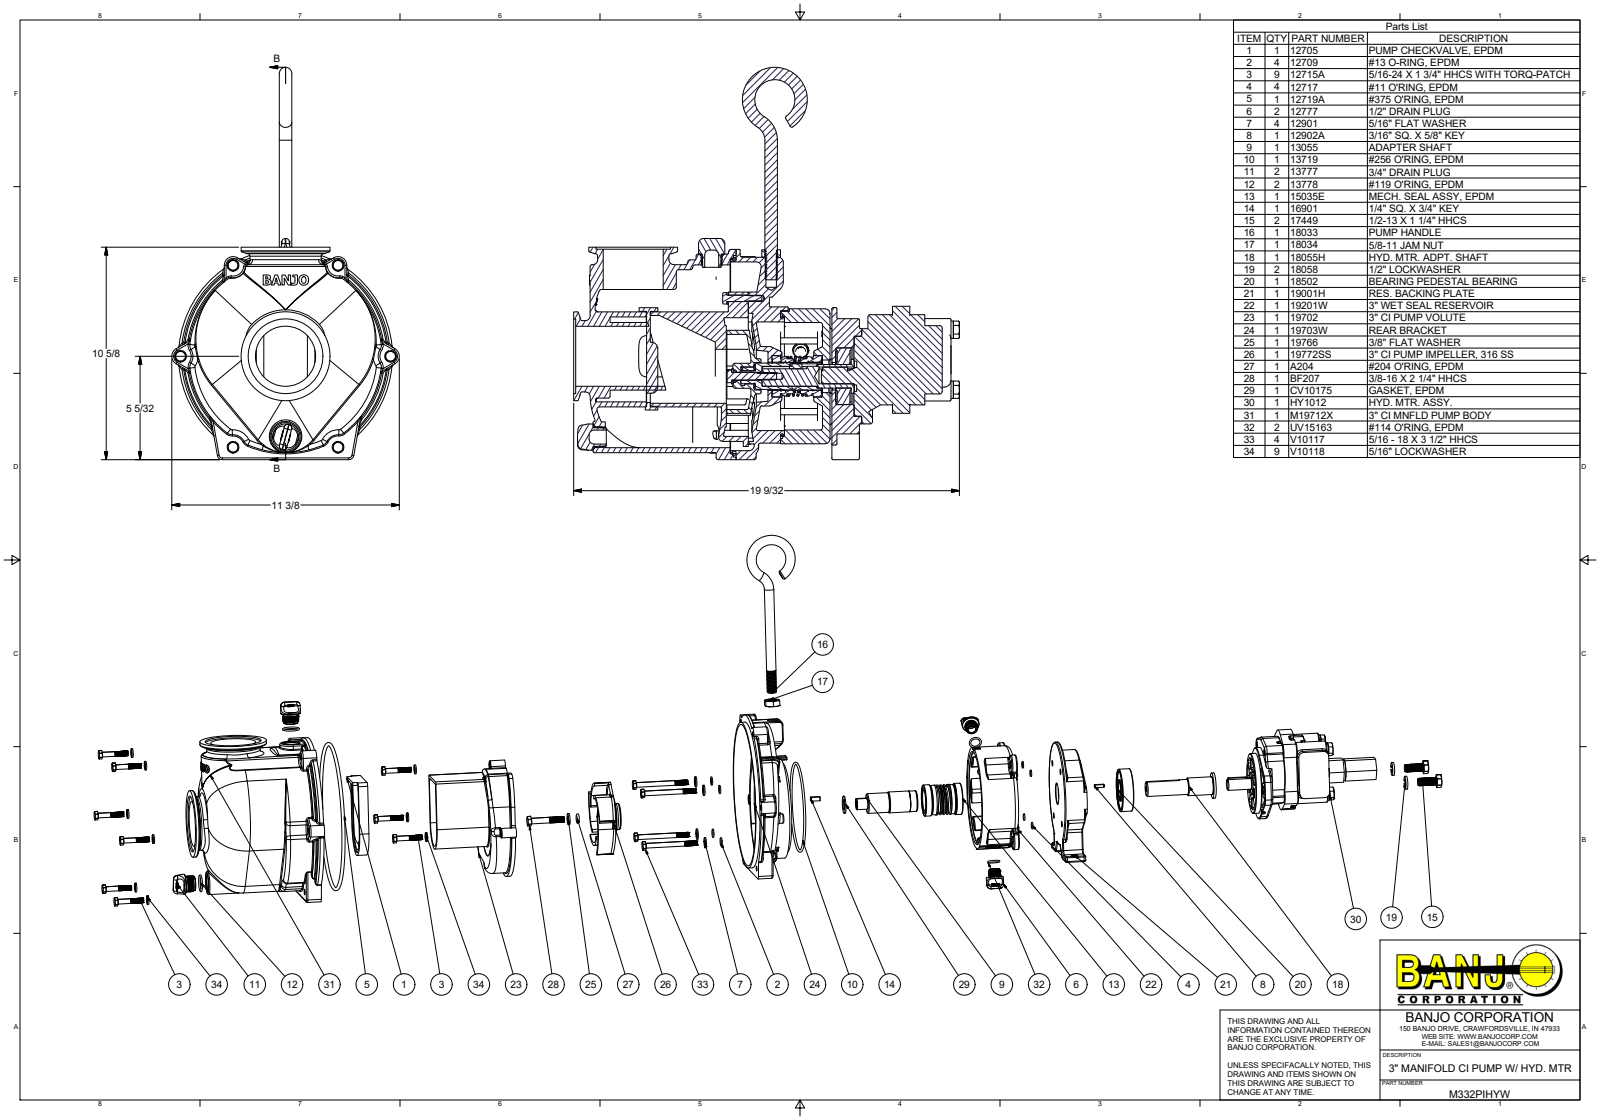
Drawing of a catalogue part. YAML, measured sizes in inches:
part_name: "M332PIHYW; 19703W; 19201W; M19712X (+8 more)"
step_written_by: "Autodesk Inventor 2012 (AUTOMOTIVE_DESIGN)"
units: inches
bodies: {solids: 74, faces: 8066, planar: 1729, cylindrical: 2662, other: 3675}
overall_size: [22.172, 19.62, 11.375]
volume: 382.9
surface_area: 2361
round_holes:
  - {diameter: 0.267, count: 9}
  - {diameter: 0.322, count: 9}
  - {diameter: 0.323, count: 9}
  - {diameter: 0.252, count: 4}
  - {diameter: 0.313, count: 4}
  - {diameter: 0.32, count: 4}
  - {diameter: 0.344, count: 4}
  - {diameter: 0.425, count: 4}
  - {diameter: 0.437, count: 4}
  - {diameter: 0.516, count: 4}
  - {diameter: 0.531, count: 4}
  - {diameter: 0.56, count: 4}
round_bosses_or_shafts:
  - {diameter: 0.276, count: 180}
  - {diameter: 0.268, count: 60}
  - {diameter: 0.436, count: 30}
  - {diameter: 0.324, count: 15}
  - {diameter: 0.313, count: 13}
  - {diameter: 0.583, count: 9}
  - {diameter: 0.73, count: 6}
  - {diameter: 0.5, count: 6}
partial_cylinders:
  - {radius: 0.06, count: 237}
  - {radius: 0.125, count: 125}
  - {radius: 0.09, count: 96}
  - {radius: 0.12, count: 84}
  - {radius: 0.03, count: 61}
  - {radius: 0.25, count: 34}
  - {radius: 0.5, count: 29}
  - {radius: 0.138, count: 18}
face_to_face_distances: [0.25, 4.787, 4.178, 0.094, 4.694, 0.375, 5.087, 2.225, 2.469, 2.563]
hole_center_spacings: [4.404, 5.25, 1.125, 1.521, 3.354, 3.536, 4.968, 5.126]
